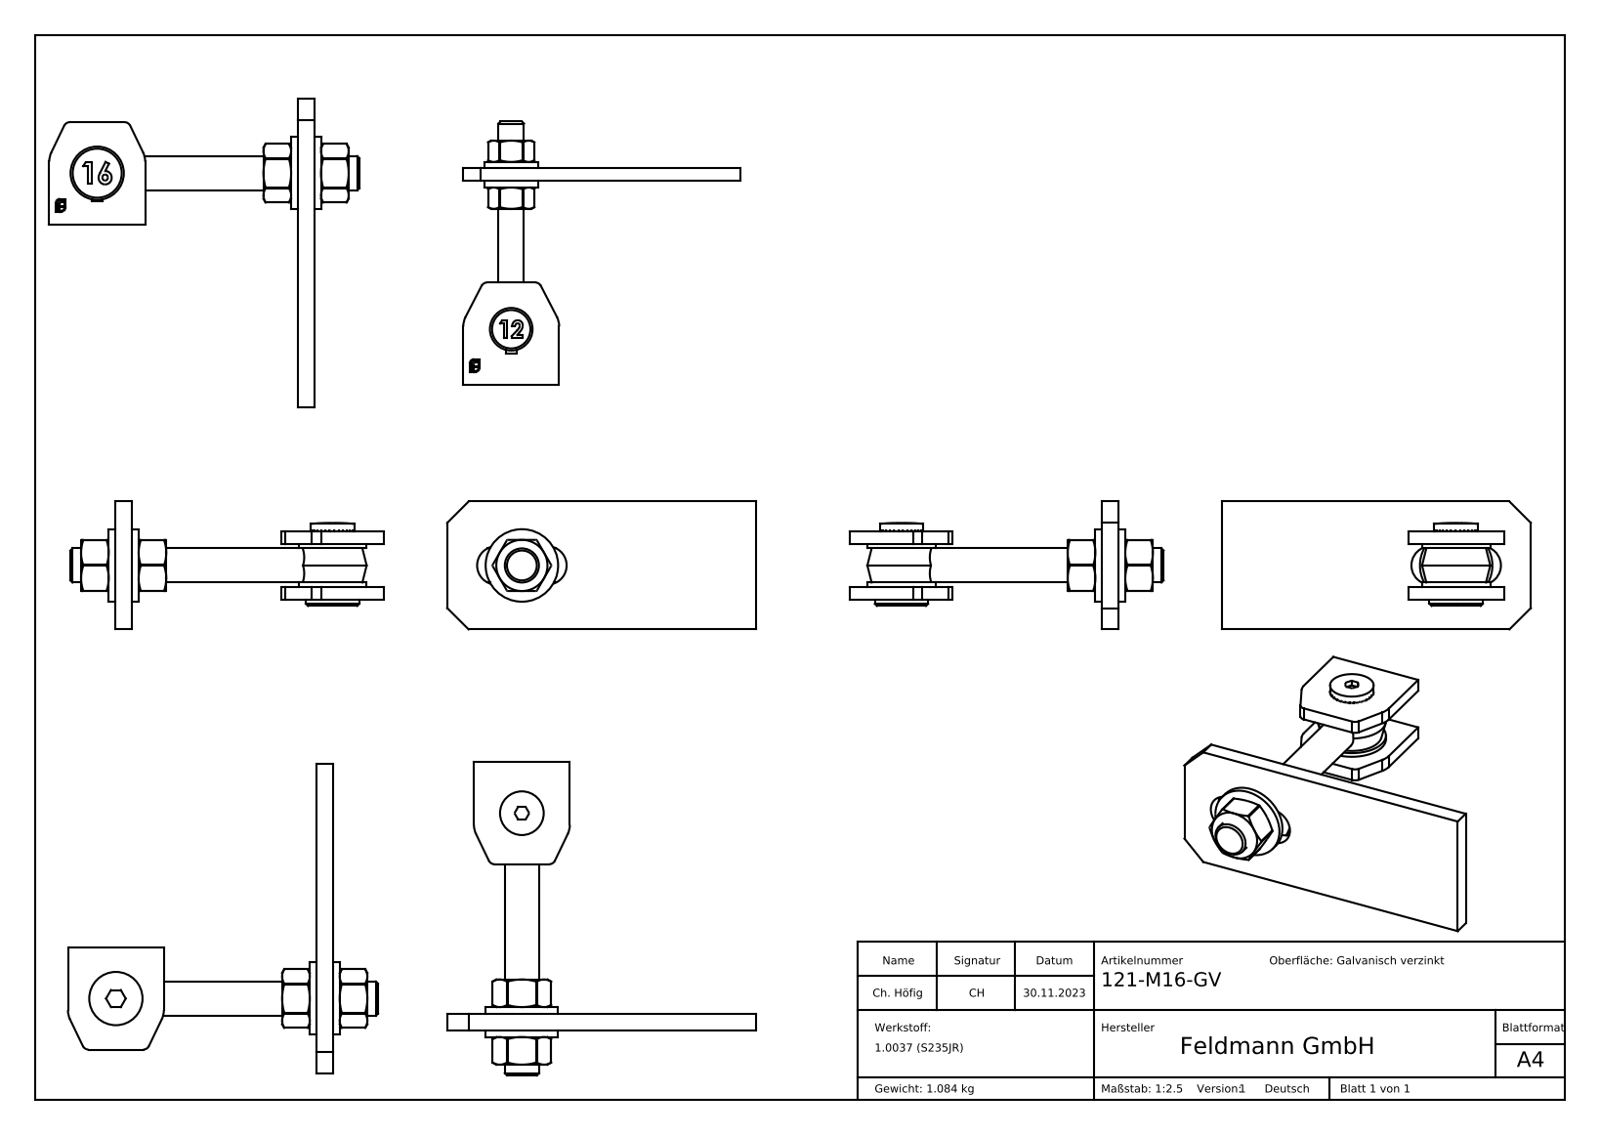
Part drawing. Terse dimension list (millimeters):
name: Torband Teil3_121-M16-GV Teil3; Torband Teil5_121-M16-GV Teil5; Torband Teil4_121-M16-GV Teil4; Torband Teil2_121-M16-GV Teil2 (+6 more)
written by: SolidWorks 2018 (CONFIG_CONTROL_DESIGN)
unit: mm
bodies: 12 solids, 553 faces (355 planar, 41 cylindrical, 157 other)
size: 147.05 × 145 × 60
volume: 138 724 mm³; area: 54 086 mm²
holes: 1× ⌀5, 1× ⌀14, 1× ⌀16.5, 1× ⌀17
bosses: 1× ⌀34, 1× ⌀32, 1× ⌀25, 1× ⌀20.5, 1× ⌀16, 1× ⌀15.7, 1× ⌀6
rounds: 6× R0.5, 2× R3, 2× R9, 2× R10
face distances: 8, 20, 6, 26, 24, 14, 18, 11, 3, 2
